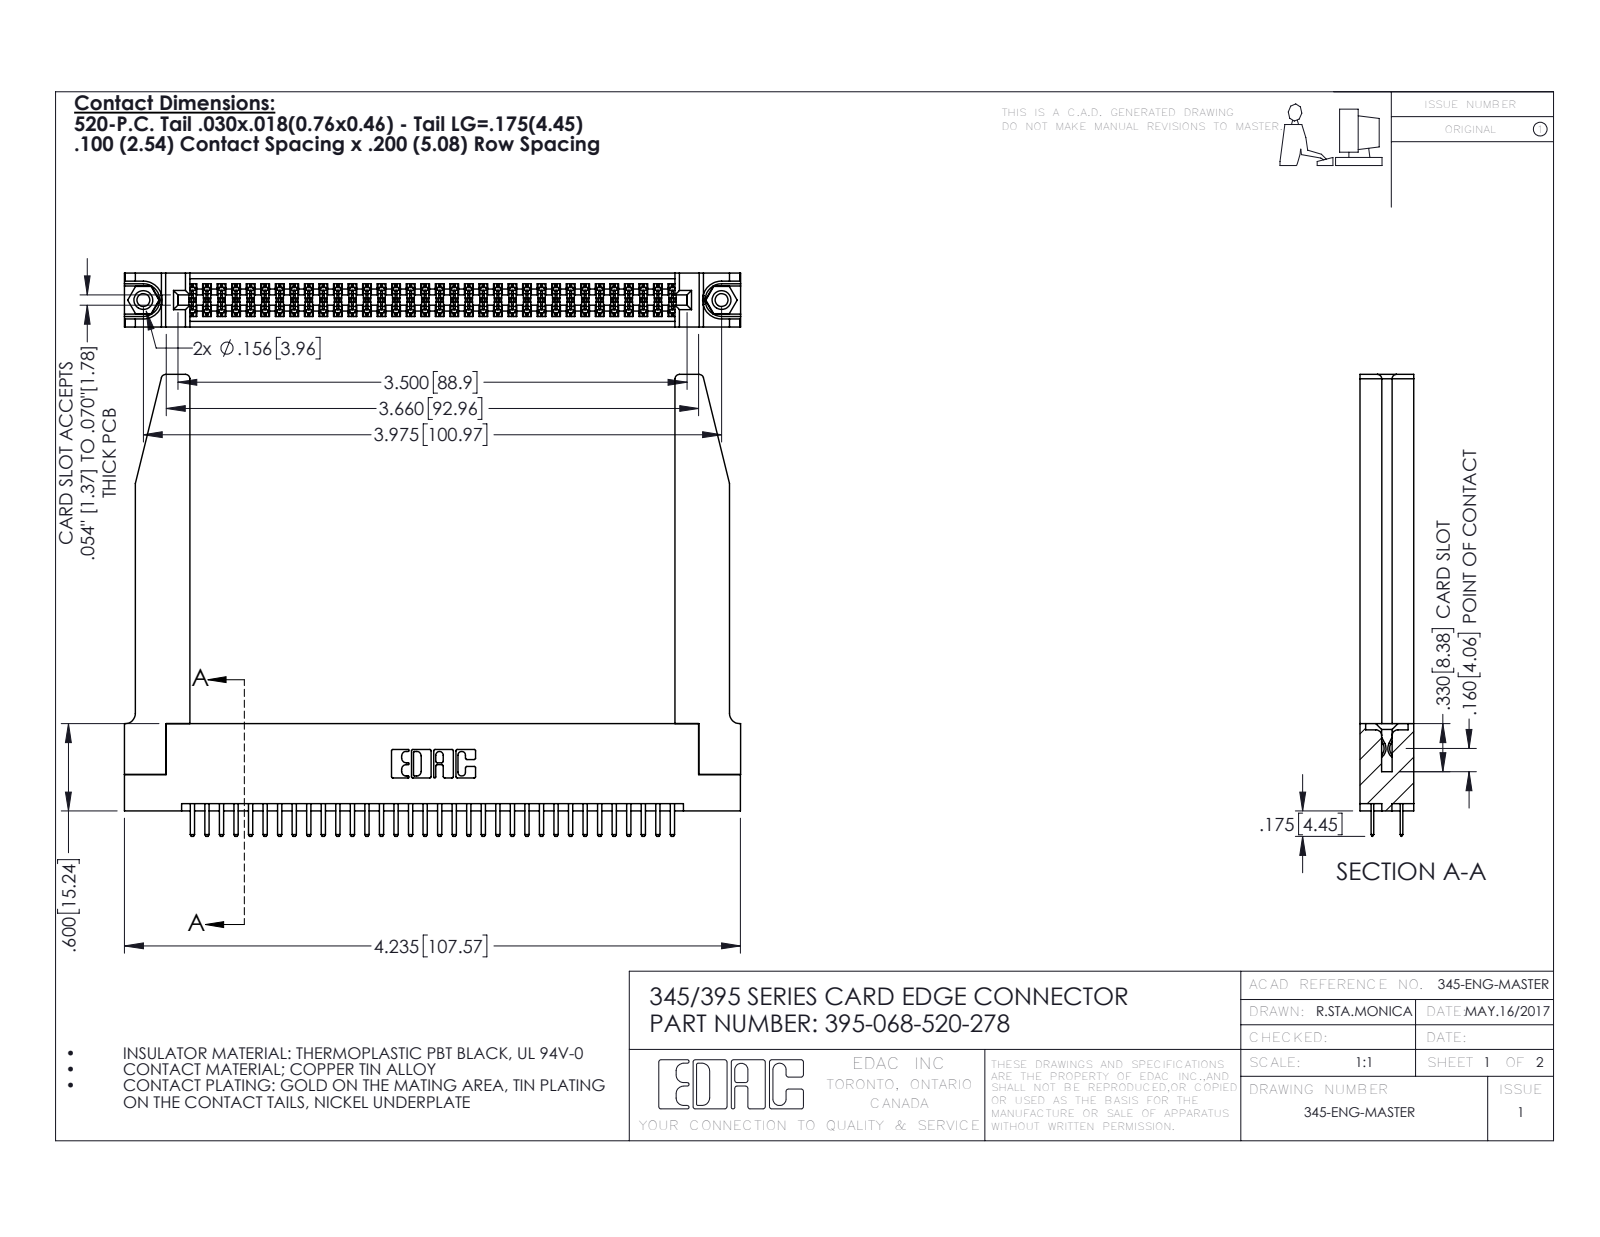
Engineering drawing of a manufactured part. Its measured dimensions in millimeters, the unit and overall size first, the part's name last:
Units: millimetres
Overall size (bounding box): 107.6 × 80.6 × 9.4
Round holes (diameter × count): ⌀2.3 ×2, ⌀3.2 ×2, ⌀4 ×2, ⌀1.6 ×1
Round bosses / shafts (diameter × count): ⌀3.9 ×2
Partial cylindrical surfaces — rounded edges, fillets, slot ends (radius × count): R0.2 ×102, R0.3 ×72, R0.3 ×22, R0.8 ×8, R0.2 ×6, R0.8 ×6, R0.7 ×3, R0.4 ×2
Main face-to-face distances: 9.4, 1.8, 7.6, 5.1, 2.5, 6.9, 0.6, 5.7, 0.6, 4.4
Hole centre spacings: 6.9, 95, 101
Volume: 18 120 mm³ · Surface area: 21 920 mm²
Bodies: 73 solids, 4032 faces (2602 planar, 1378 cylindrical, 52 other)
Part name (STEP PRODUCT): 345-220-078_345-220-078; 345-292-001_345-293-120; 345 Part_Flush Mounting Lugs - 0.156 Dia-TH; 345-250-001_345-250-001-102 (+1 more)
STEP written by: SolidWorks 2016 (CONFIG_CONTROL_DESIGN)
